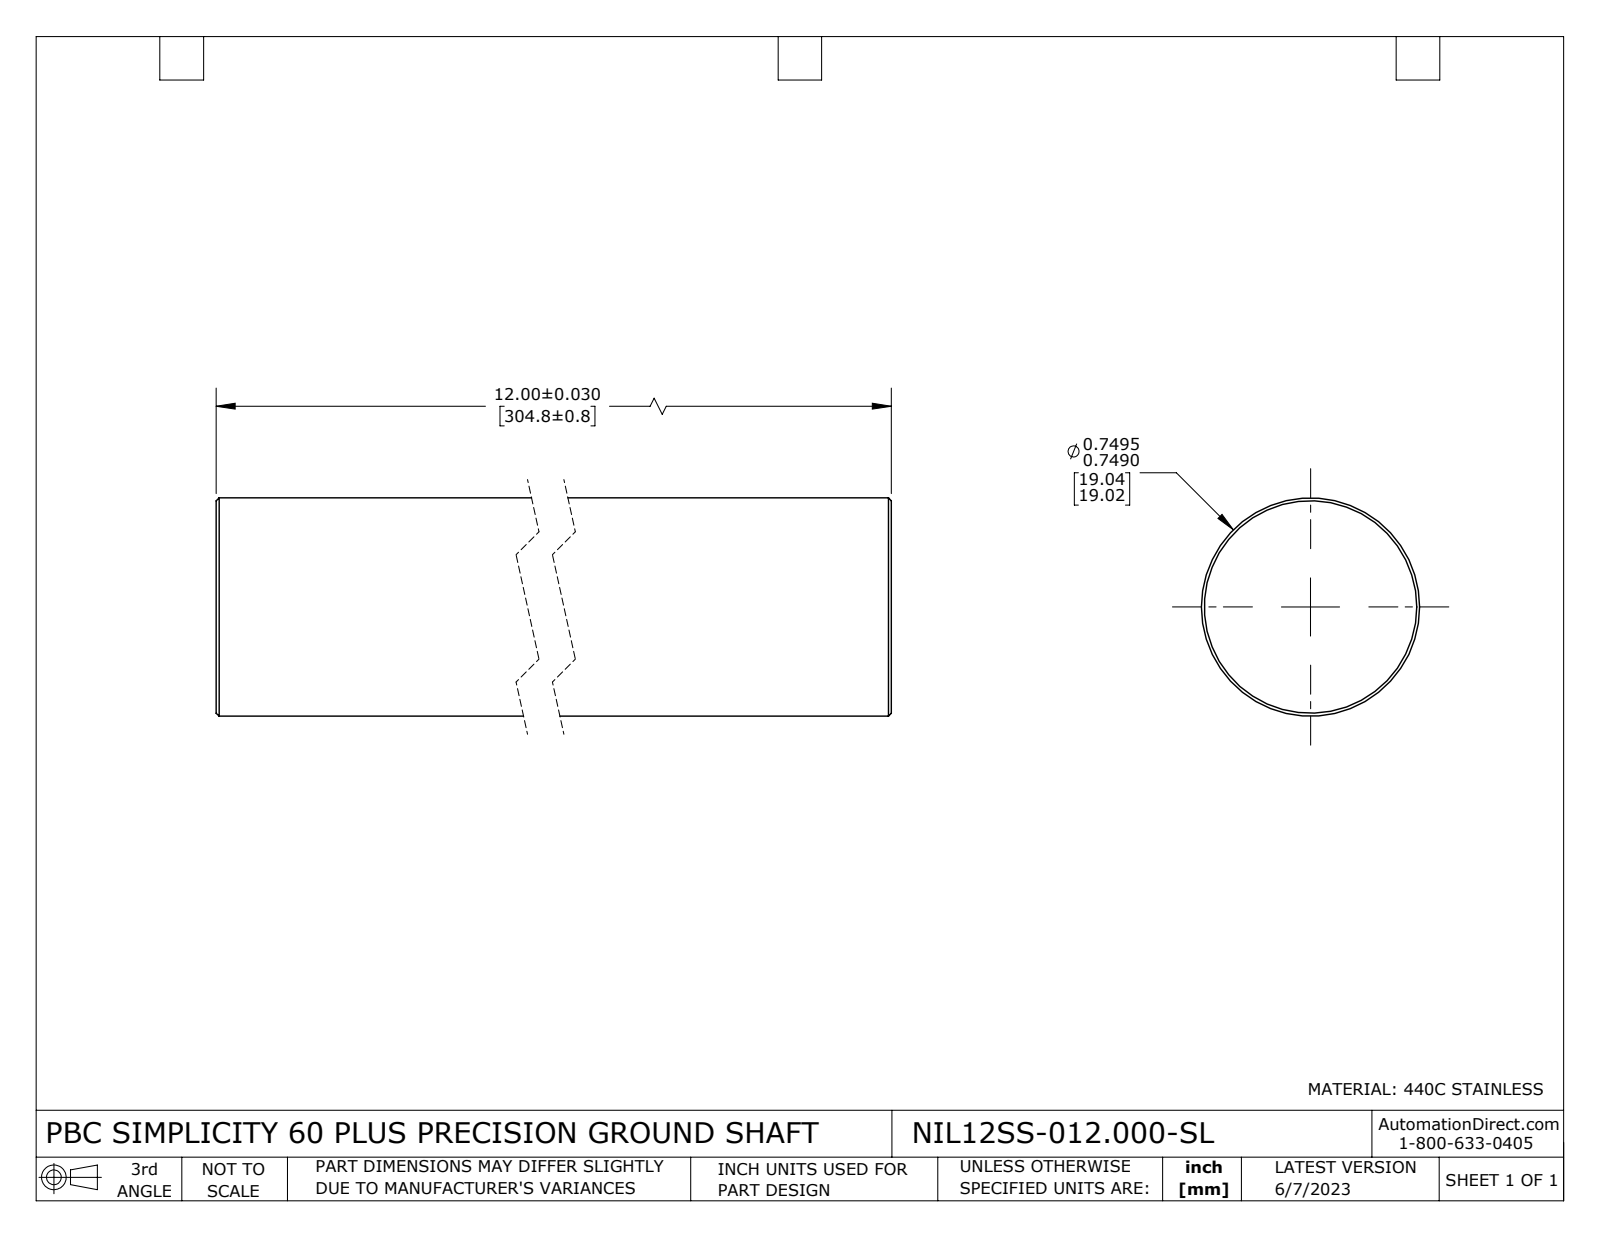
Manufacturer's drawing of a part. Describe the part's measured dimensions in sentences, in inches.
The part is named "NIL12SS-012.000-SL". Its 3-D file was written by "SolidWorks 2021 (CONFIG_CONTROL_DESIGN)". It is 1 solid with 8 faces: 2 planar, 2 cylindrical and 4 other. Overall it measures 12 by 0.75 by 0.75 inches. Its volume is 5.301 cubic inches and its surface area 29.13 square inches. Round bosses or shafts: 1 of diameter 0.75. The main face-to-face distances are 12.
